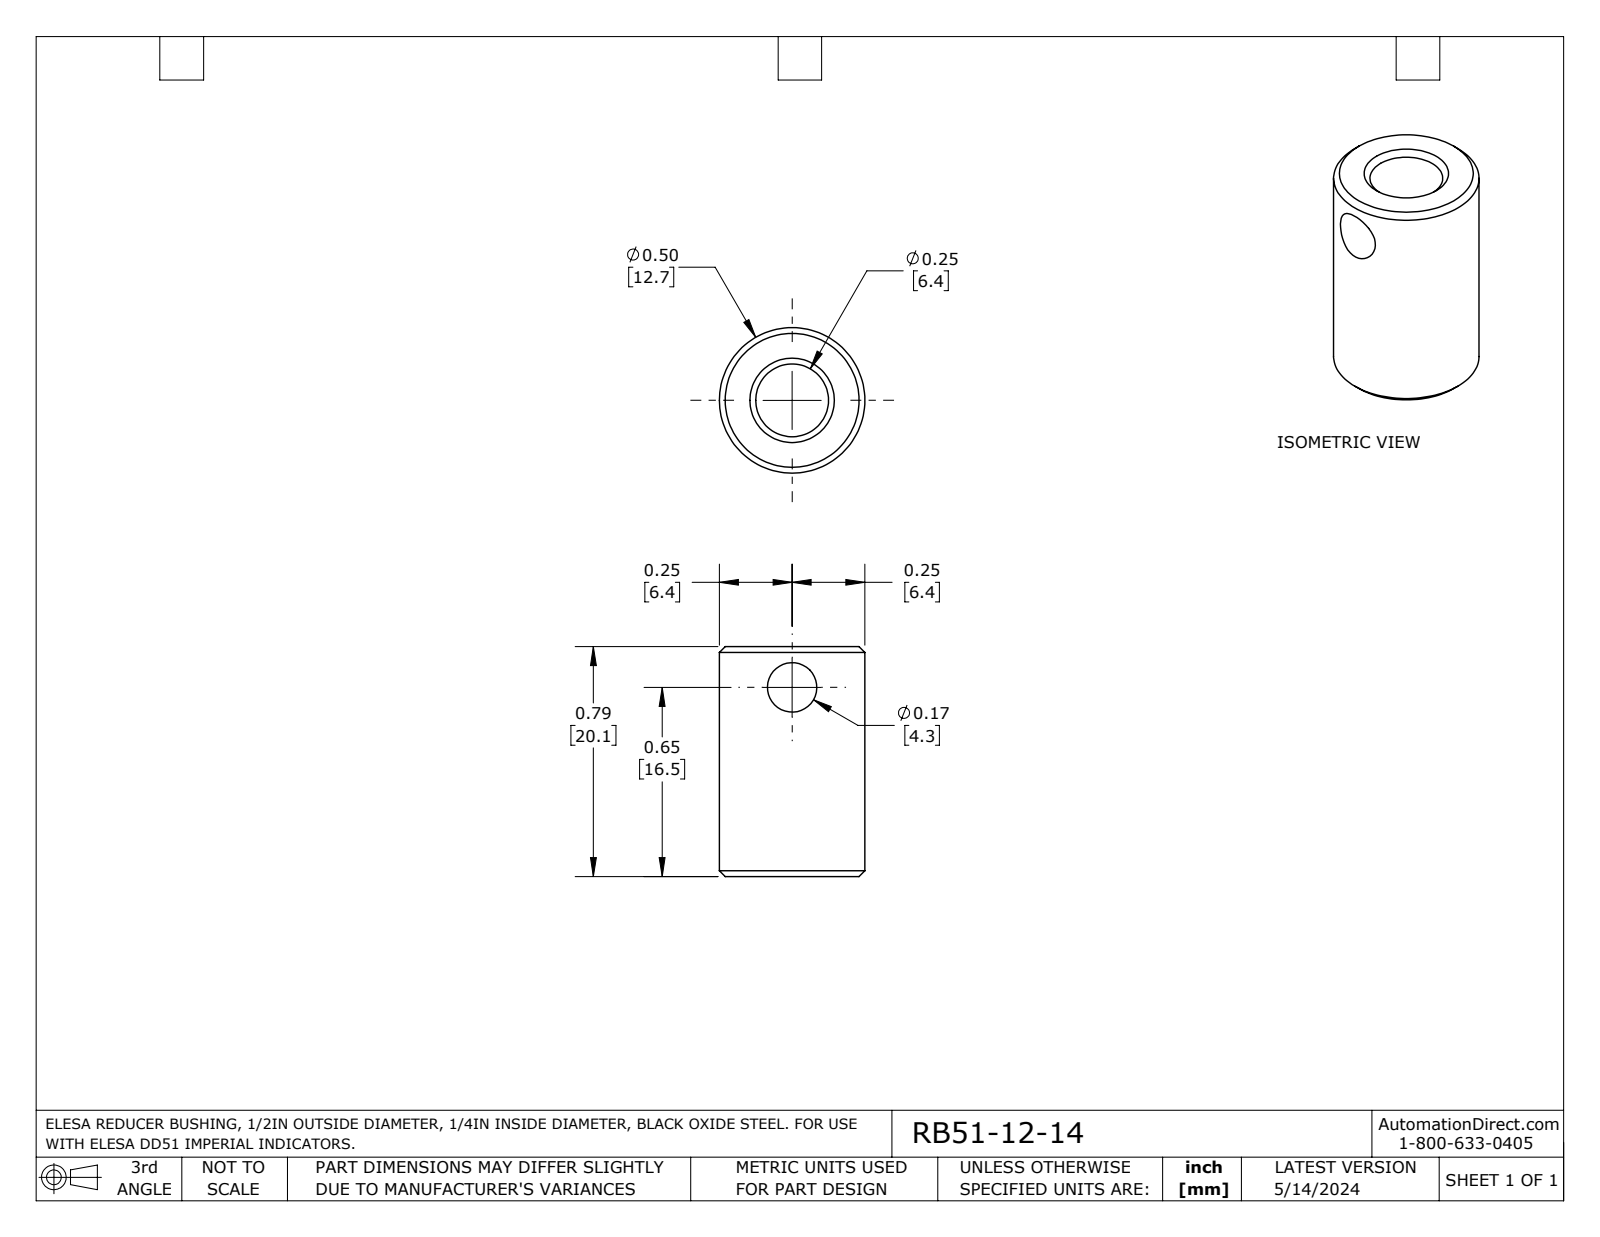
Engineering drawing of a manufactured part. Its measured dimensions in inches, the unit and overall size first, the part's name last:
Units: inches
Overall size (bounding box): 0.79 × 0.5 × 0.5
Round holes (diameter × count): ⌀0.17 ×1, ⌀0.25 ×1
Round bosses / shafts (diameter × count): ⌀0.5 ×1
Main face-to-face distances: 0.79
Volume: 0.112 in³ · Surface area: 2.125 in²
Bodies: 1 solid, 9 faces (2 planar, 3 cylindrical, 4 other)
Part name (STEP PRODUCT): RB51 1_2-1_4
STEP written by: SolidWorks 2023 (AUTOMOTIVE_DESIGN)
